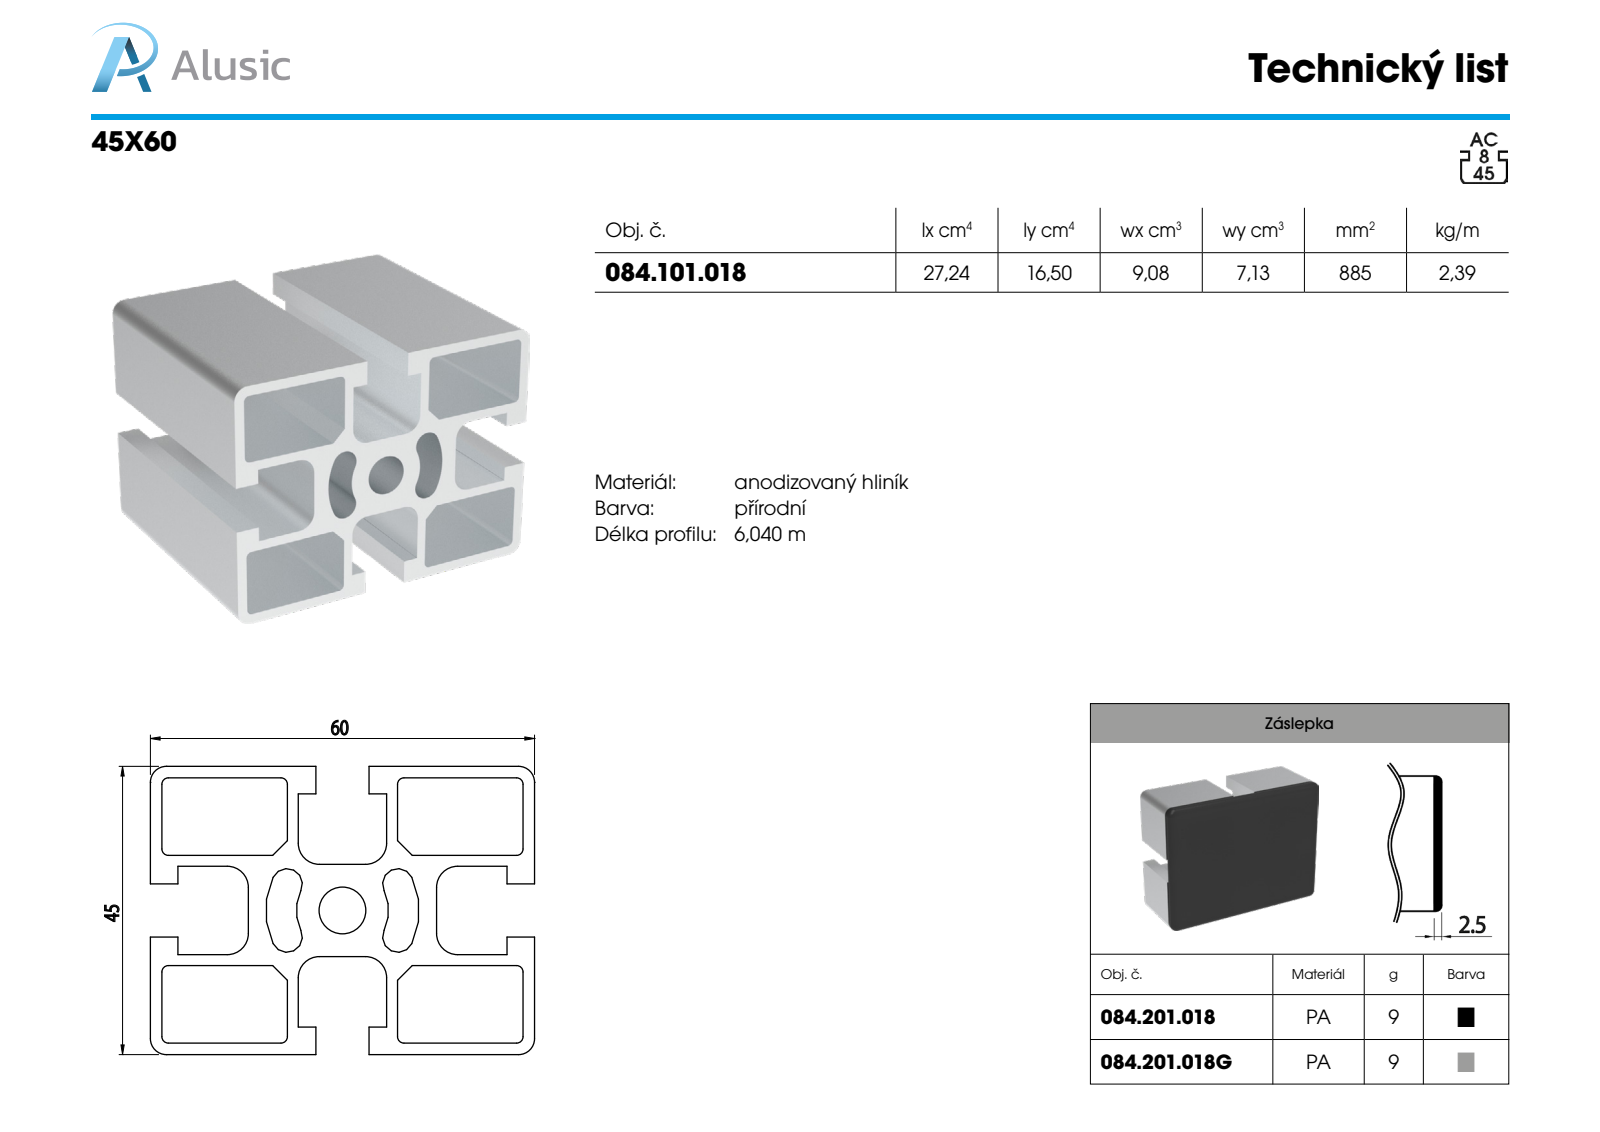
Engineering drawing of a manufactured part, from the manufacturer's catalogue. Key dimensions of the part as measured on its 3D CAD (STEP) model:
Part name (STEP PRODUCT): 084.101.018
STEP written by: SolidWorks 2018 (AUTOMOTIVE_DESIGN)
Units: millimetres
Bodies: 1 solid, 173 faces (94 planar, 79 cylindrical, 0 other)
Overall size (bounding box): 100 × 60 × 45
Volume: 82 612 mm³ · Surface area: 72 258 mm²
Round holes (diameter × count): ⌀7.3 ×1
Partial cylindrical surfaces — rounded edges, fillets, slot ends (radius × count): R2.5 ×28, R0.1 ×12, R1 ×12, R3.2 ×8, R2.4 ×4, R7.2 ×1, R12 ×1
Main face-to-face distances: 1.5, 14.1, 15.3, 29.4, 21.6, 13.8, 36.9, 43.5, 45, 23.1
